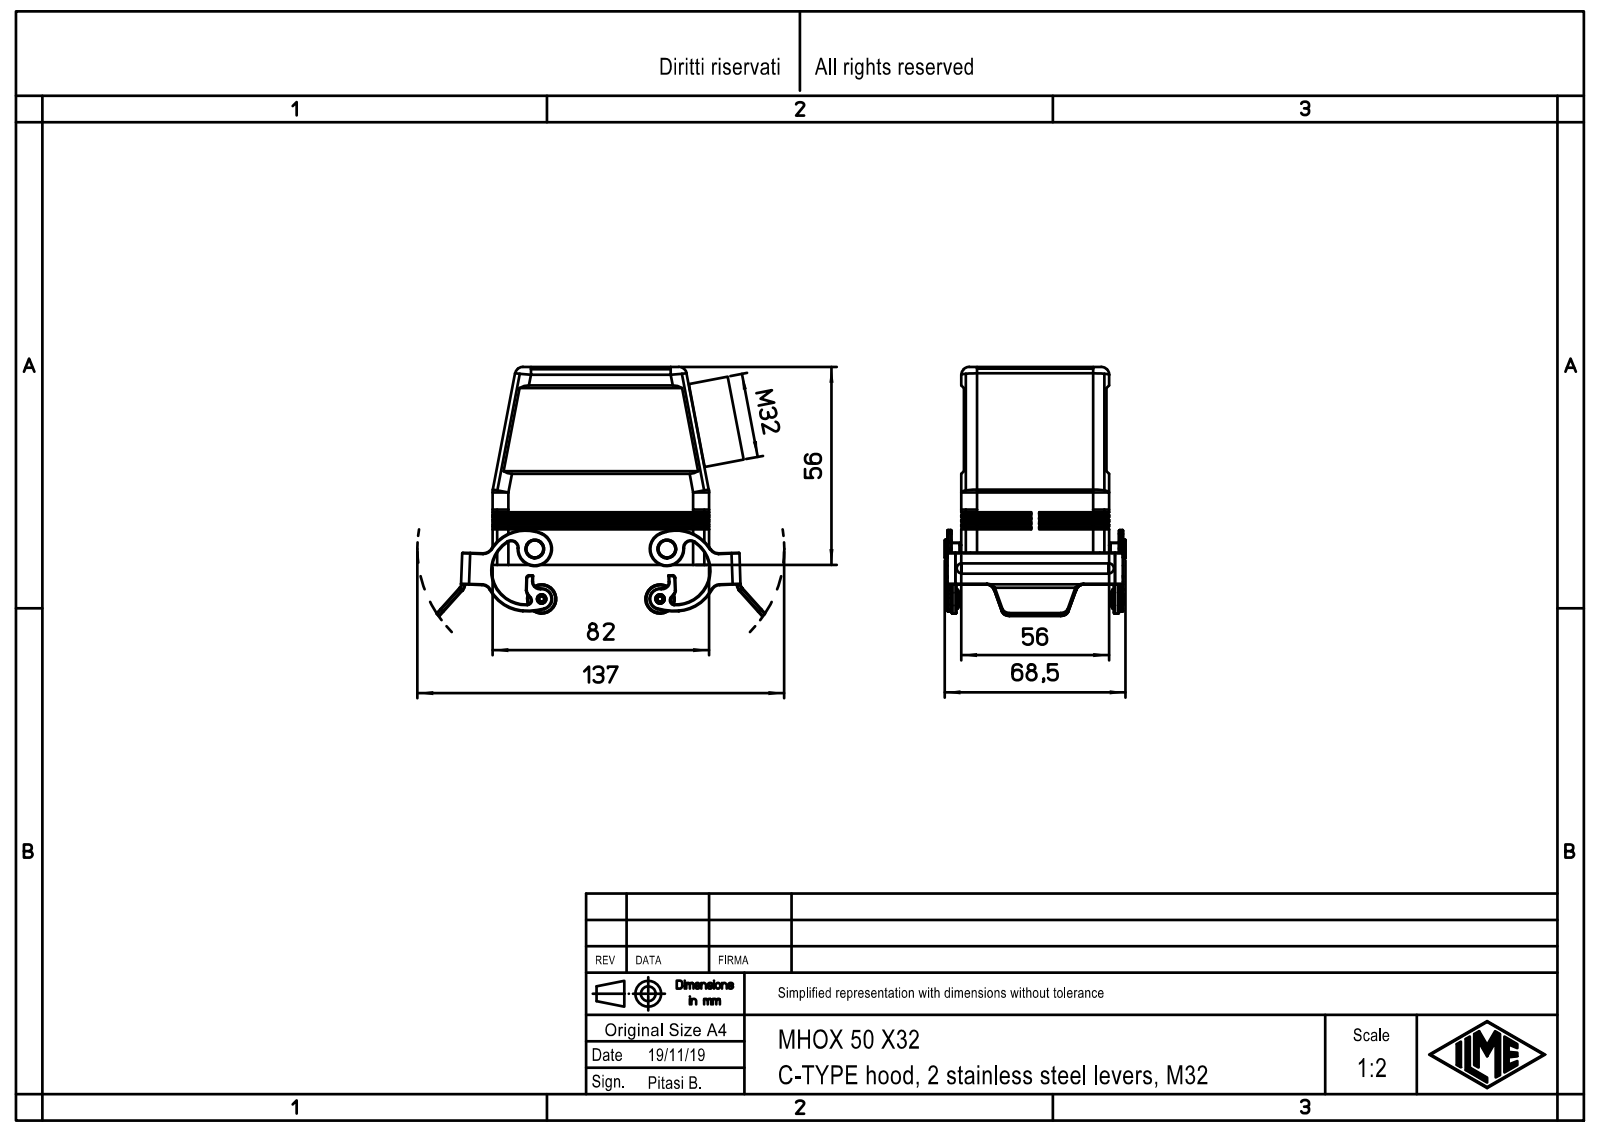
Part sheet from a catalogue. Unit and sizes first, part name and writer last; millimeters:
Units: millimetres
Overall size (bounding box): 124.33 × 82.61 × 68.5
Round holes (diameter × count): ⌀3.5 ×8, ⌀5 ×4, ⌀2 ×2, ⌀3.1 ×2, ⌀32 ×1
Round bosses / shafts (diameter × count): ⌀7 ×4, ⌀4.8 ×4, ⌀11 ×2, ⌀3.5 ×2, ⌀3 ×2, ⌀36 ×1
Partial cylindrical surfaces — rounded edges, fillets, slot ends (radius × count): R3 ×18, R2 ×16, R0.5 ×12, R3.5 ×10, R6.5 ×7, R1.5 ×6, R2.5 ×4, R4 ×4
Main face-to-face distances: 2.9, 1.5, 65, 7.91, 10.81, 103.41, 66.5, 52.64, 55.54, 63.5
Hole centre spacings: 16, 24.2, 66, 67.91, 70.3, 8.2, 19.08, 40.2
Volume: 72 843 mm³ · Surface area: 51 871 mm²
Bodies: 7 solids, 584 faces (221 planar, 239 cylindrical, 124 other)
Part name (STEP PRODUCT): Leva; CHPX 50.21.1; CHPX 50.21.3; Leva.1 (+4 more)
STEP written by: Creo Elements/Direct Modeling 20.1B 02-Apr-2019 (C) Parametric Technology GmbH (AUTOMOTIVE_DESIGN)
